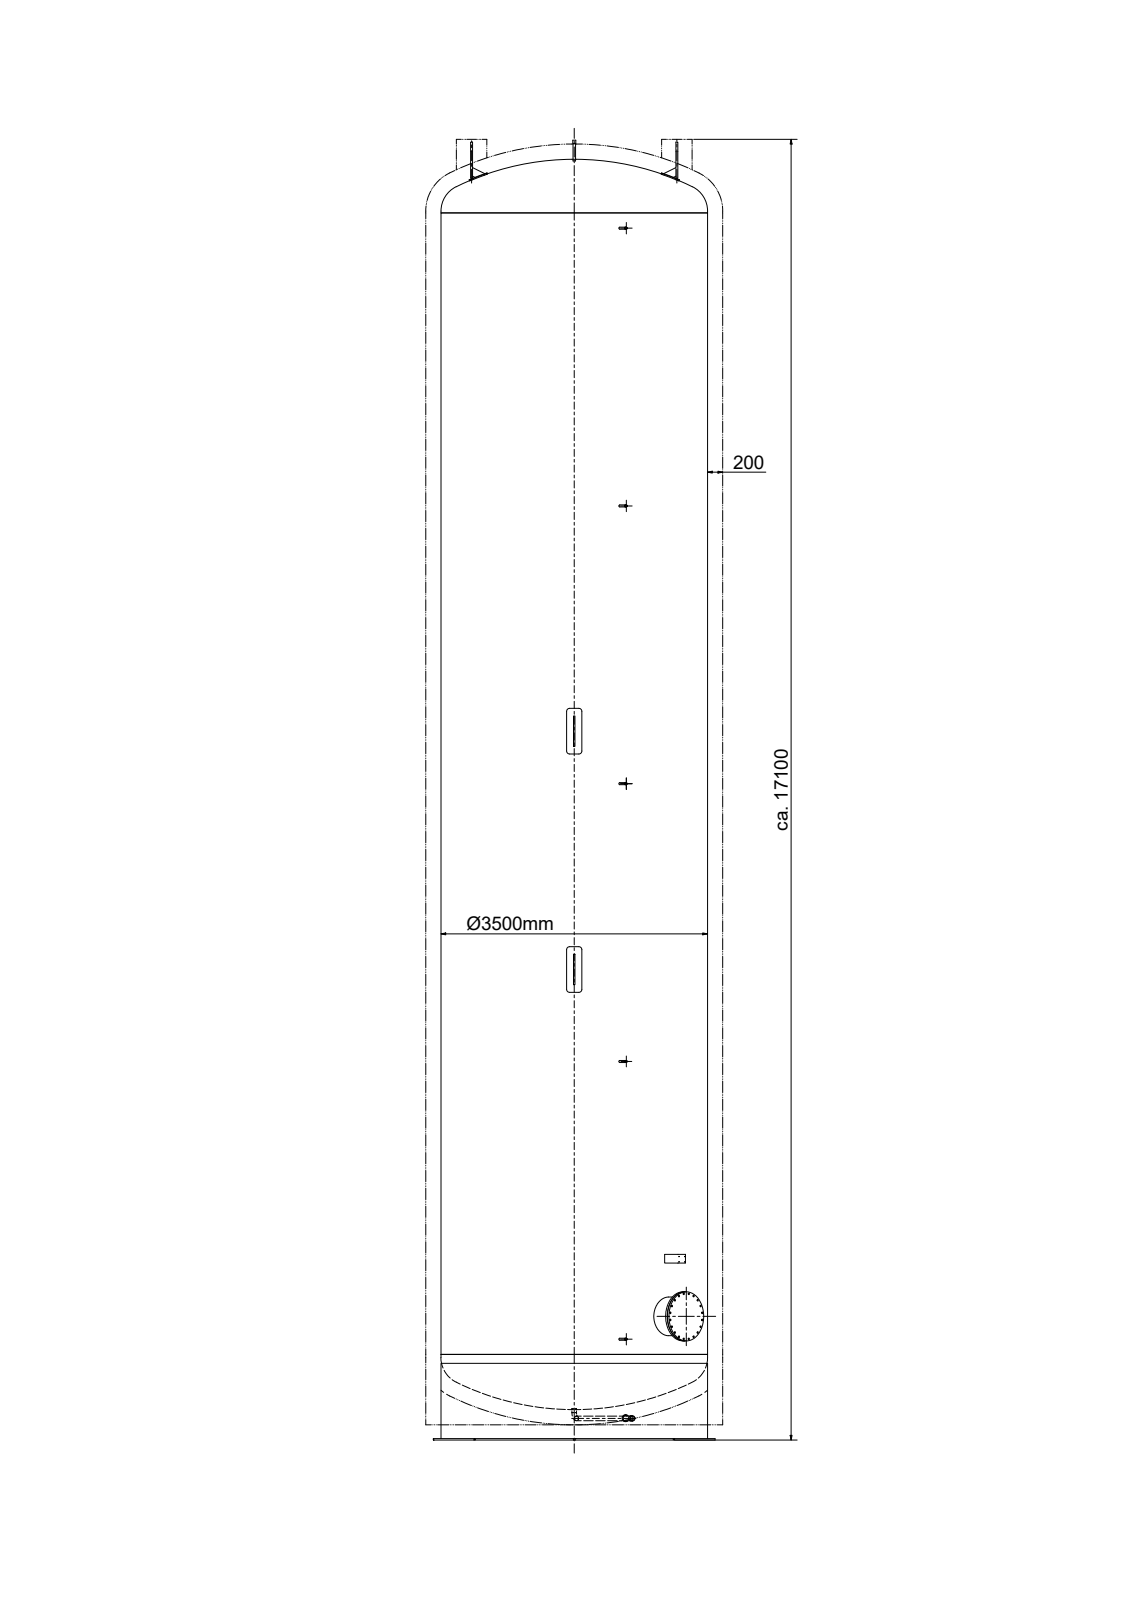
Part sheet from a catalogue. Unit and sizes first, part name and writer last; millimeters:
Units: millimetres
Overall size (bounding box): 17081.76 × 3741.96 × 3699.92
Round holes (diameter × count): ⌀22 ×80, ⌀18.63 ×5, ⌀21.7 ×5, ⌀26.9 ×5, ⌀5.8 ×4, ⌀206.5 ×4, ⌀207.3 ×4, ⌀219.1 ×4, ⌀52.3 ×2, ⌀72 ×2, ⌀508 ×2, ⌀27.3 ×1
Round bosses / shafts (diameter × count): ⌀219.1 ×8, ⌀26.9 ×5, ⌀26.4 ×5, ⌀340 ×4, ⌀268 ×4, ⌀645 ×2, ⌀3700 ×1, ⌀3500 ×1
Partial cylindrical surfaces — rounded edges, fillets, slot ends (radius × count): R12 ×8, R40 ×8, R42 ×8, R5 ×2, R10 ×2, R72 ×2, R125 ×1, R1762 ×1
Main face-to-face distances: 20, 600, 200, 191, 171, 180, 9, 6950, 8050, 8075.43
Hole centre spacings: 300, 147.5, 93.86, 185.41, 352.67, 3650, 592.61, 485.41
Volume: 2 132 000 000 mm³ · Surface area: 427 800 000 mm²
Bodies: 50 solids, 426 faces (172 planar, 226 cylindrical, 28 other)
Part name (STEP PRODUCT): Ø3500_152_3_200_SZ_WZ2; Klöpper_Gew_Ø3500_6,4; Klöpper_Gew_Ø3500_10,6; Zyl_Ø3500_8x15000_2019 (+8 more)
STEP written by: Autodesk Inventor 2019 (AUTOMOTIVE_DESIGN)
